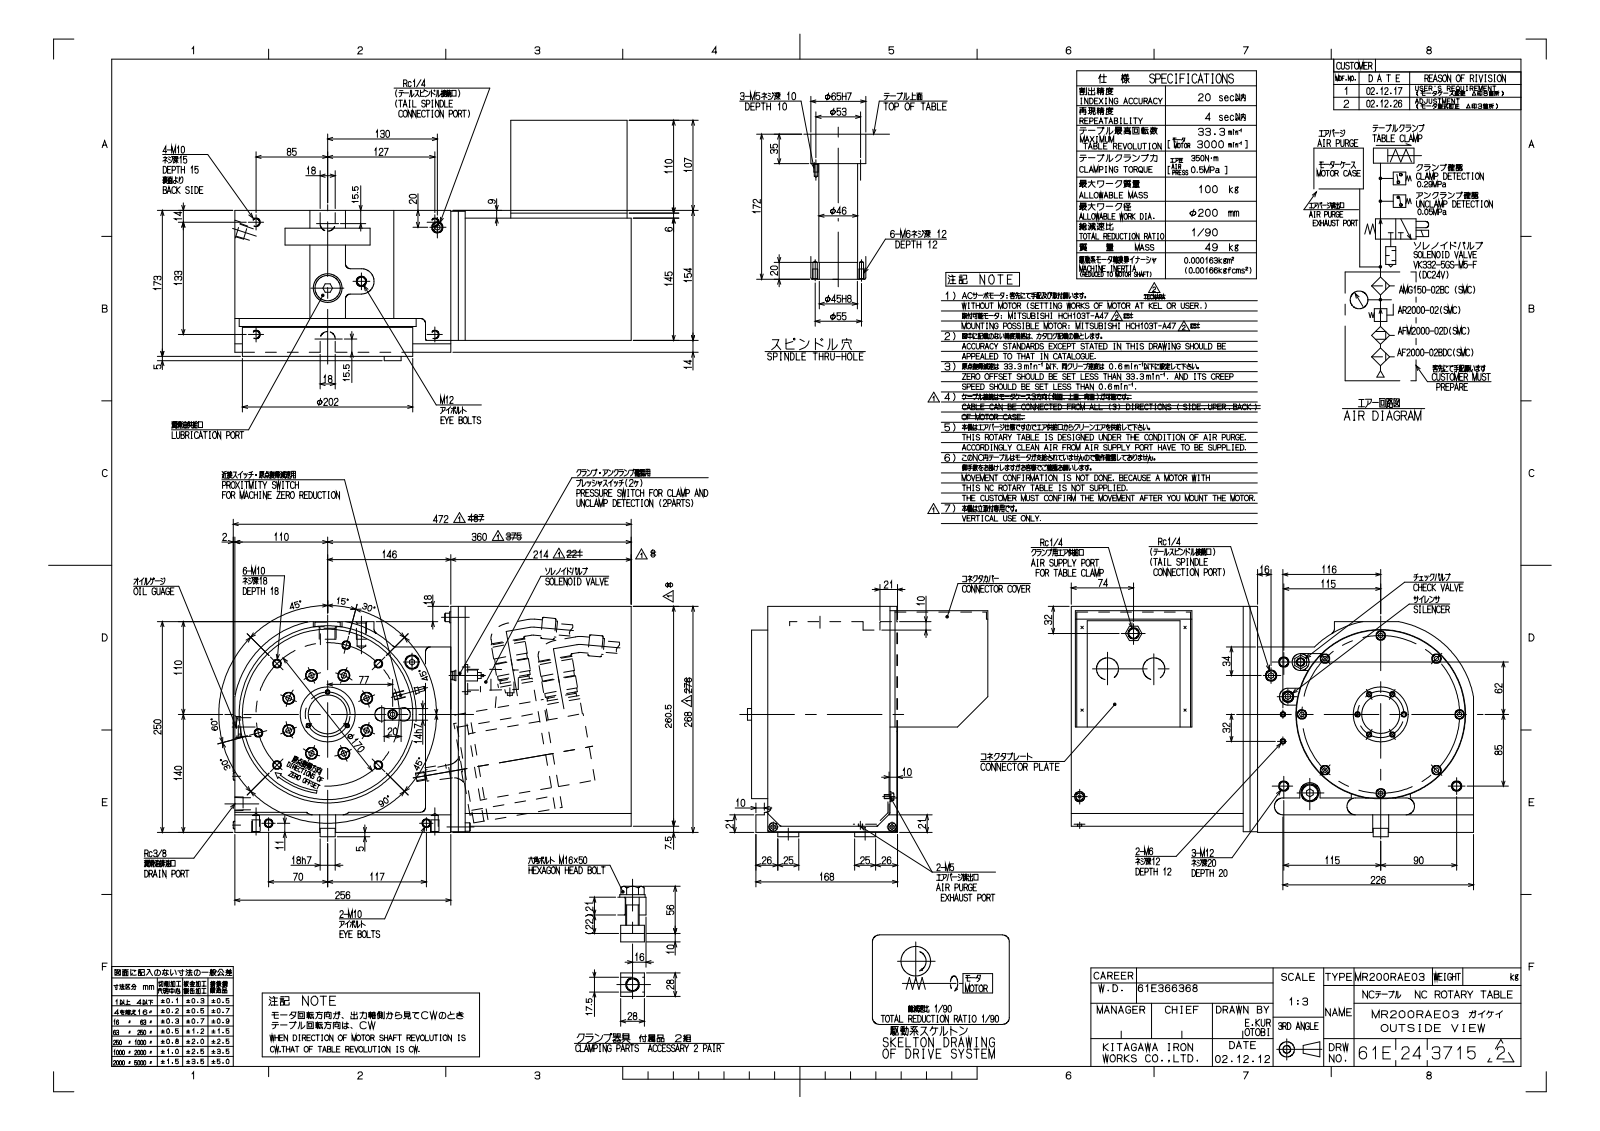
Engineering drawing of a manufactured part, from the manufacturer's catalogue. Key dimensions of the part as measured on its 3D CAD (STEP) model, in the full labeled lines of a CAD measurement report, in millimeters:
Part name (STEP PRODUCT): OUTSIDE VIEW(61E2487944)MR200RAY05
STEP written by: SolidWorks 2014 (CONFIG_CONTROL_DESIGN)
Units: millimetres
Bodies: 6 solids, 1063 faces (524 planar, 410 cylindrical, 129 other)
Overall size (bounding box): 421.7 × 285 × 283
Volume: 13 380 000 mm³ · Surface area: 774 200 mm²
Round holes (diameter × count): ⌀5 ×33, ⌀6 ×20, ⌀8.5 ×14, ⌀10 ×14, ⌀11 ×11, ⌀14 ×9, ⌀10.2 ×4, ⌀12 ×4, ⌀4.2 ×3, ⌀16 ×2, ⌀21 ×2, ⌀108 ×2
Round bosses / shafts (diameter × count): ⌀10 ×15, ⌀13 ×8, ⌀9 ×7, ⌀12 ×4, ⌀32 ×2, ⌀18.6 ×2, ⌀213 ×1, ⌀207 ×1
Partial cylindrical surfaces — rounded edges, fillets, slot ends (radius × count): R10 ×23, R6 ×4, R8 ×2, R8.5 ×2, R9 ×1, R12 ×1, R15 ×1, R43.5 ×1
Main face-to-face distances: 5, 8, 1.6, 156, 151, 14, 153, 6.6, 1, 9
Hole centre spacings: 27.5, 83.4, 45.2, 45.2, 59, 83.4, 93.5, 109
